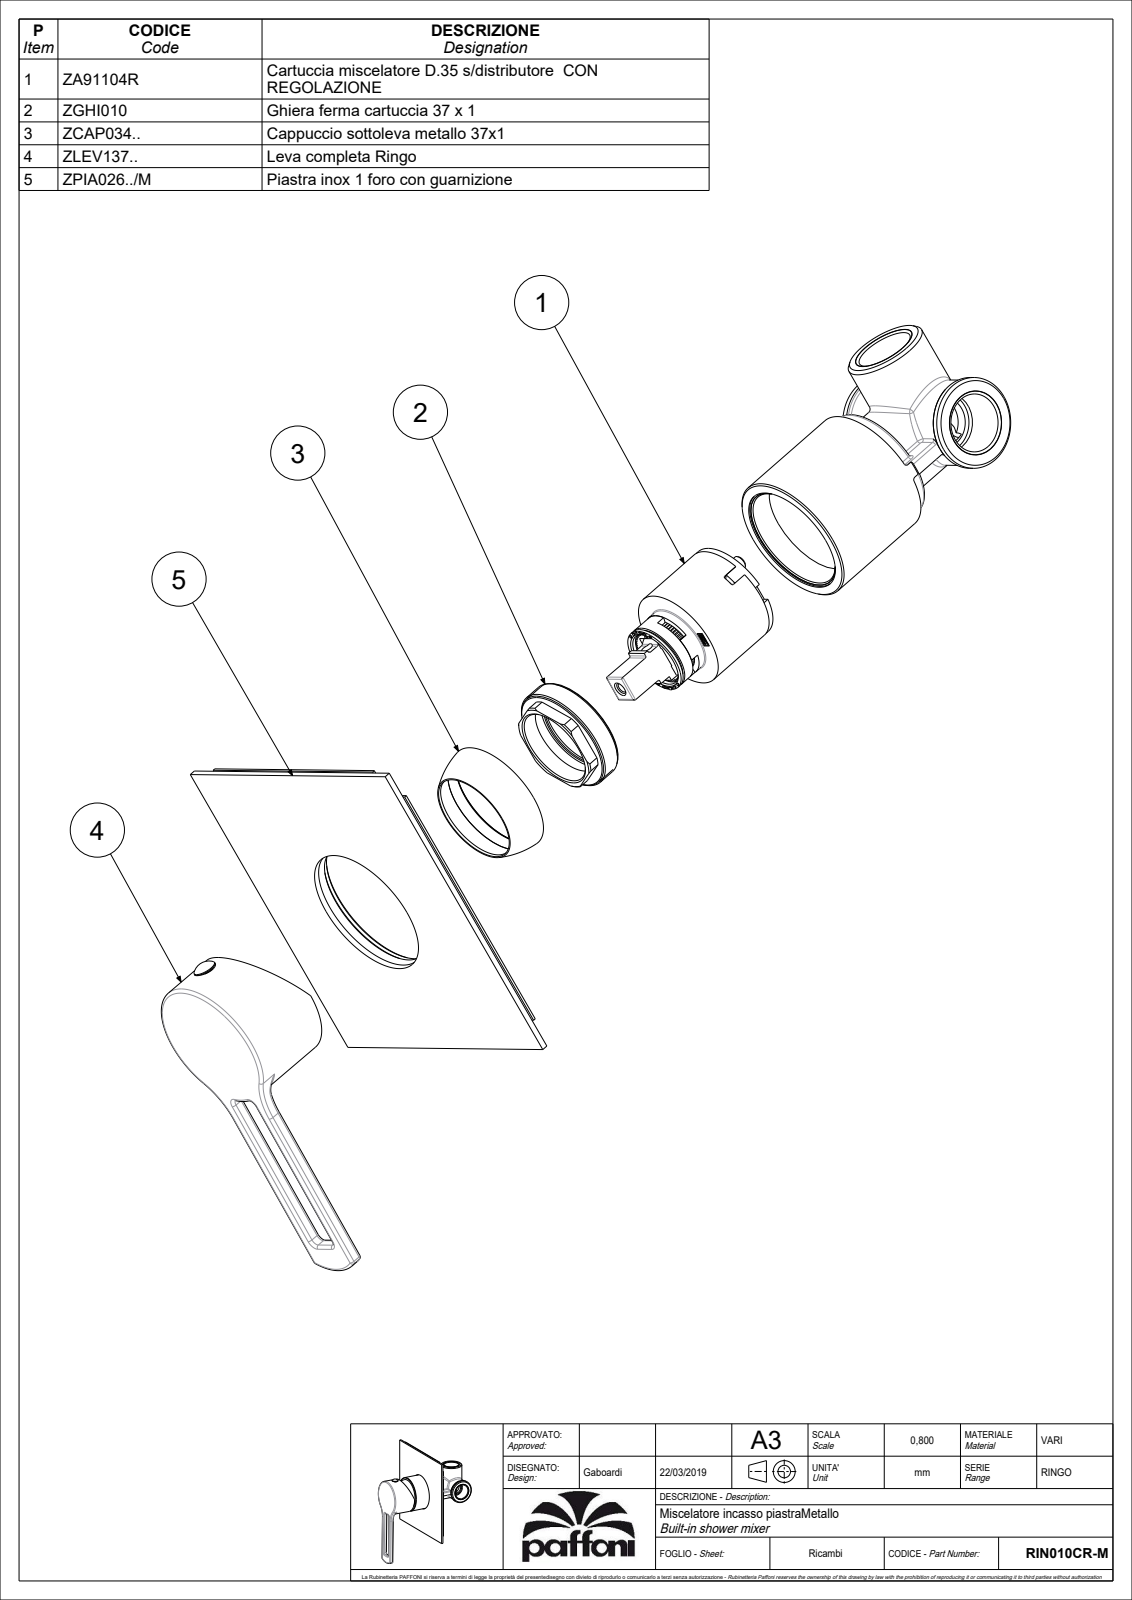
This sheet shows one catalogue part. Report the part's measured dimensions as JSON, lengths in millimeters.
{"part_name": "RIN010CR-M", "step_written_by": "CREO PARAMETRIC BY PTC INC, 2020044 (CONFIG_CONTROL_DESIGN)", "units": "millimeters", "bodies": {"solids": 2, "faces": 950, "planar": 554, "cylindrical": 207, "other": 189}, "overall_size": [144.95, 110, 53.6], "volume_mm3": 64037, "surface_area_mm2": 55557, "round_holes": [[4, 2], [3, 1], [3.3, 1], [5, 1], [7.8, 1], [19.5, 1], [19.9, 1], [26.8, 1], [29, 1], [31, 1], [32.4, 1], [36, 1]], "round_bosses_or_shafts": [[44.8, 2], [35, 1], [23.5, 1], [23.4, 1], [21.8, 1], [7.6, 1], [5.5, 1], [5, 1]], "partial_cylinders_radius": [[1, 14], [0.5, 13], [0.15, 11], [0.3, 4], [2, 4], [20, 2], [7, 1], [9.3, 1]], "face_to_face_distances": [2, 53.6, 51.6, 4.5, 1, 1.5, 3.5, 50.1, 48.1, 49.1], "hole_center_spacings": [11]}
